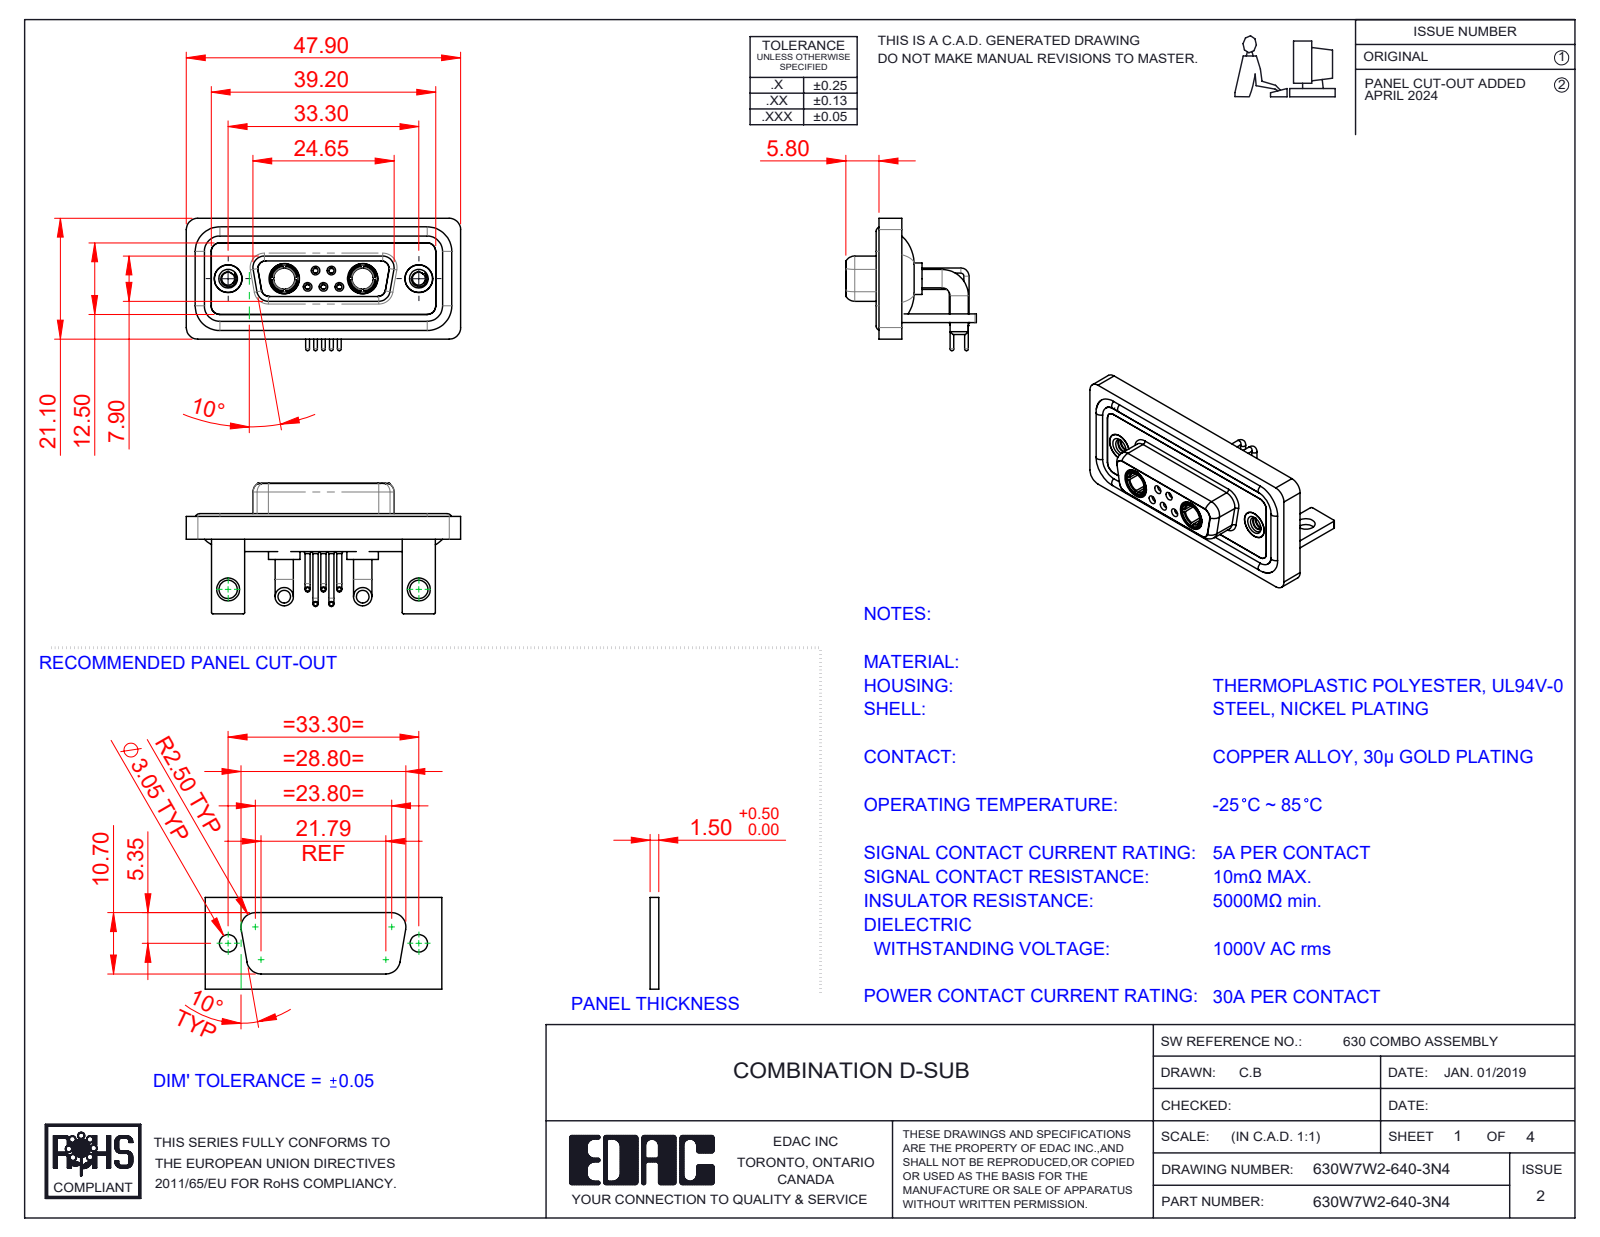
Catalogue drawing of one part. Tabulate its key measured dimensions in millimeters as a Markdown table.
| quantity | value |
| --- | --- |
| part name | 630Combo Shell Rear_15 Contacts; 630Combo Housing_7W2; 630W7W2-640-3N4; Power Socket_30A RA (+6 more) |
| STEP written by | SolidWorks 2023 (CONFIG_CONTROL_DESIGN) |
| units | millimeters |
| bodies | 18 solids, 855 faces (258 planar, 377 cylindrical, 220 other) |
| overall size | 47.9 × 23.12 × 22.8 |
| volume | 6 619 mm³ |
| surface area | 10 978 mm² |
| round holes (diameter × count) | 0.9 × 5, 1.1 × 5, 1.5 × 5, 2 × 5, 4.85 × 4, 1.6 × 3, 1.7 × 2, 2.26 × 2, 3.2 × 2, 3.7 × 2, 4 × 2, 4.05 × 2 |
| round bosses / shafts (diameter × count) | 1.6 × 6, 0.9 × 5, 0.65 × 5, 3.2 × 4, 5.5 × 2, 5.2 × 2, 4.96 × 2, 4.95 × 2 |
| partial cylindrical surfaces (radius × count) | 2 × 21, 1.5 × 18, 0.25 × 16, 1.35 × 12, 1.6 × 8, 0.5 × 5, 0.6 × 4, 0.65 × 4 |
| main face-to-face distances | 0.4, 2.9, 1.5, 1.8, 3.7, 1.1, 4.1, 1.6, 2.5, 1.4 |
| hole center spacings | 3.16, 2.77, 9.8, 23.5, 33.3, 4.31, 4.33, 5.03 |
